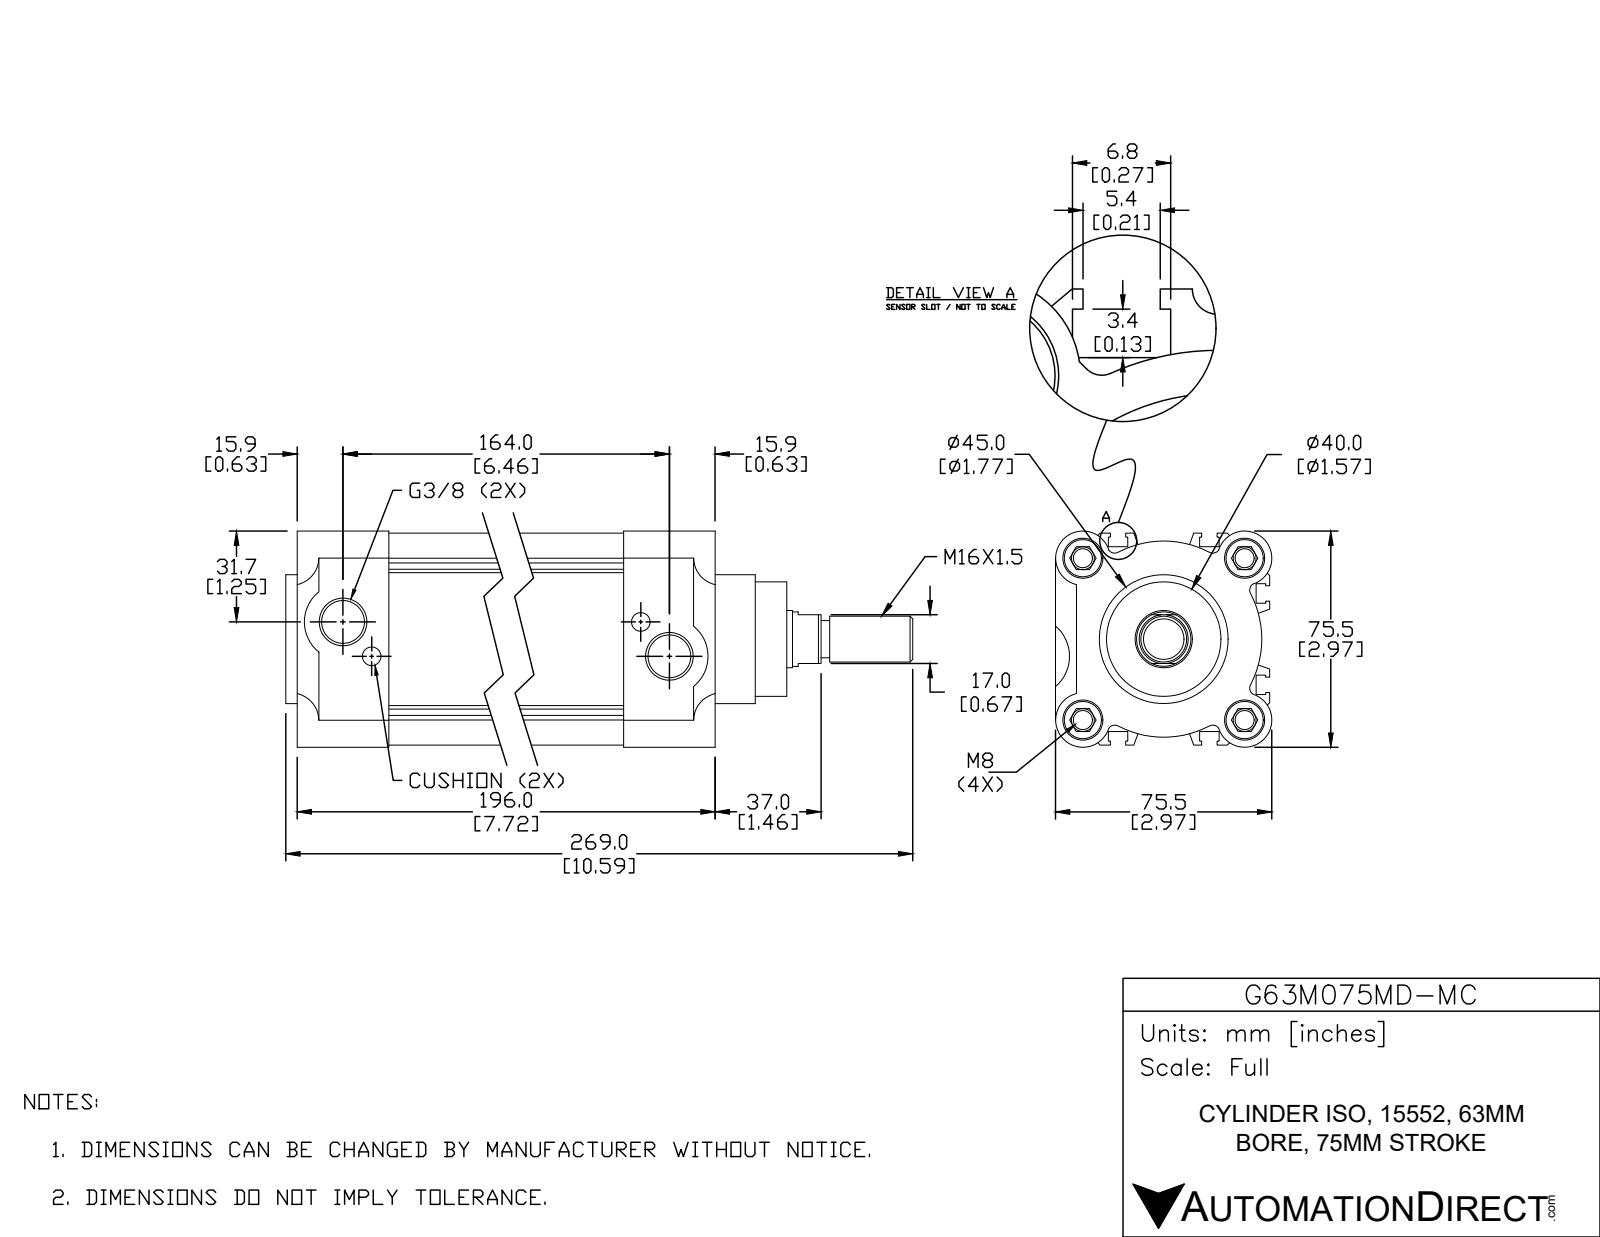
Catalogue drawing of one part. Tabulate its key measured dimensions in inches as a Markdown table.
| quantity | value |
| --- | --- |
| part name | G63M075MD-MC; 63-HL; 63121-HR; 6312175-R (+1 more) |
| STEP written by | SolidWorks 2015 (CONFIG_CONTROL_DESIGN) |
| units | inches |
| bodies | 4 solids, 422 faces (240 planar, 138 cylindrical, 44 other) |
| overall size | 10.591 × 2.974 × 2.972 |
| volume | 48.37 in³ |
| surface area | 273.6 in² |
| round holes (diameter × count) | 0.262 × 4, 0.551 × 4, 0.256 × 2, 0.262 × 2, 0.589 × 2, 0.787 × 1 |
| round bosses / shafts (diameter × count) | 0.512 × 5, 2.48 × 1, 1.772 × 1, 1.575 × 1, 0.748 × 1, 0.63 × 1 |
| partial cylindrical surfaces (radius × count) | 0.004 × 6, 0.098 × 6, 0.344 × 4, 0.374 × 4, 0.531 × 2, 1.339 × 1, 1.348 × 1 |
| main face-to-face distances | 0.354, 4.843, 0.187, 1.26, 1.614, 6.102, 6.457, 3.307, 2.726, 5.197 |
| hole center spacings | 1.573, 2.224, 0.615, 3.146, 6.063, 5.689, 6.474 |
